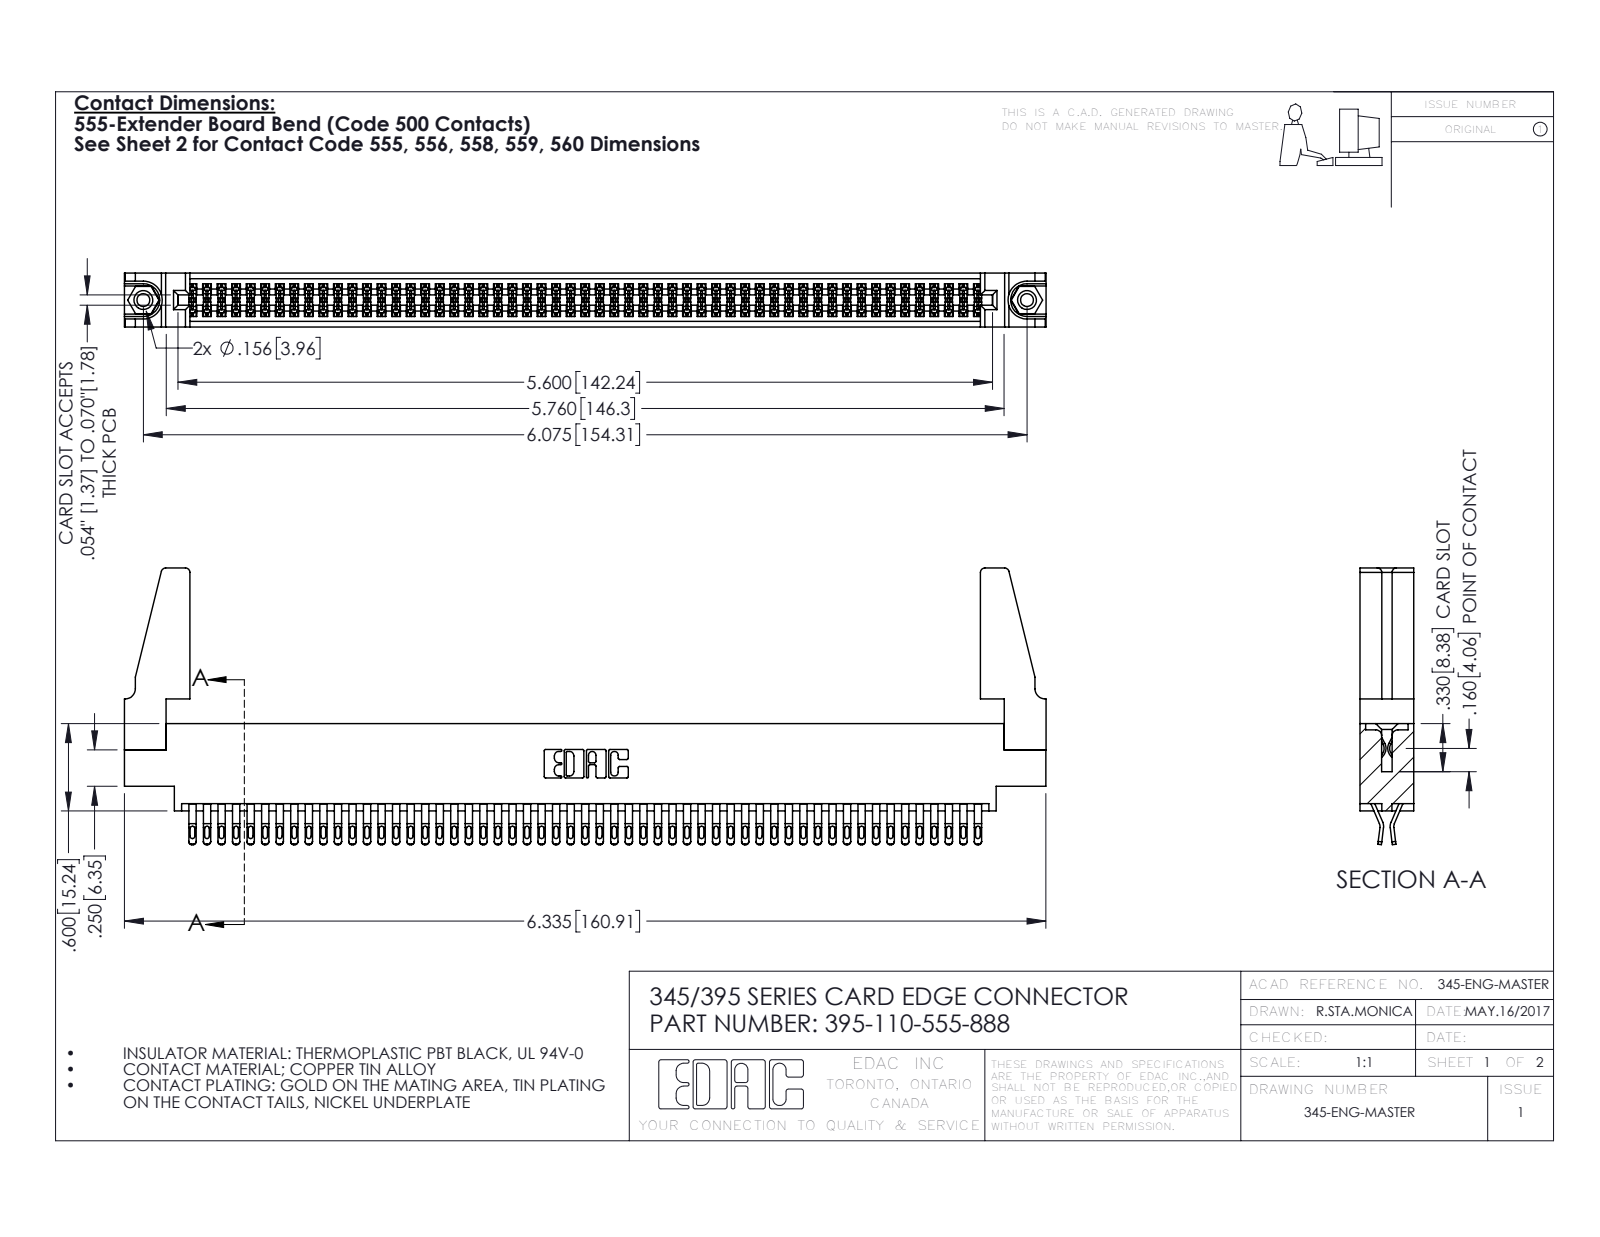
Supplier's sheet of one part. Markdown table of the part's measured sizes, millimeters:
| quantity | value |
| --- | --- |
| part name | 345-292-001_555 Tail; 345-250-001_345-250-001-102; 345-220-078_345-220-088; 395-110-555-888 (+1 more) |
| STEP written by | SolidWorks 2016 (CONFIG_CONTROL_DESIGN) |
| units | millimeters |
| bodies | 115 solids, 6414 faces (3566 planar, 2832 cylindrical, 16 other) |
| overall size | 160.9 × 48.3 × 9.4 |
| volume | 19 210 mm³ |
| surface area | 28 220 mm² |
| round holes (diameter × count) | 2.3 × 2, 3.2 × 2, 4 × 2, 1.6 × 1 |
| round bosses / shafts (diameter × count) | 3.9 × 2 |
| partial cylindrical surfaces (radius × count) | 0.4 × 275, 0.5 × 220, 0.2 × 165, 0.3 × 22, 0.8 × 8, 0.2 × 6, 0.8 × 6, 0.7 × 3 |
| main face-to-face distances | 1.8, 7.6, 9.4, 0.6, 5.1, 2.5, 6.9, 5.7, 4.4, 3.8 |
| hole center spacings | 6.9, 148.3, 154.3 |
